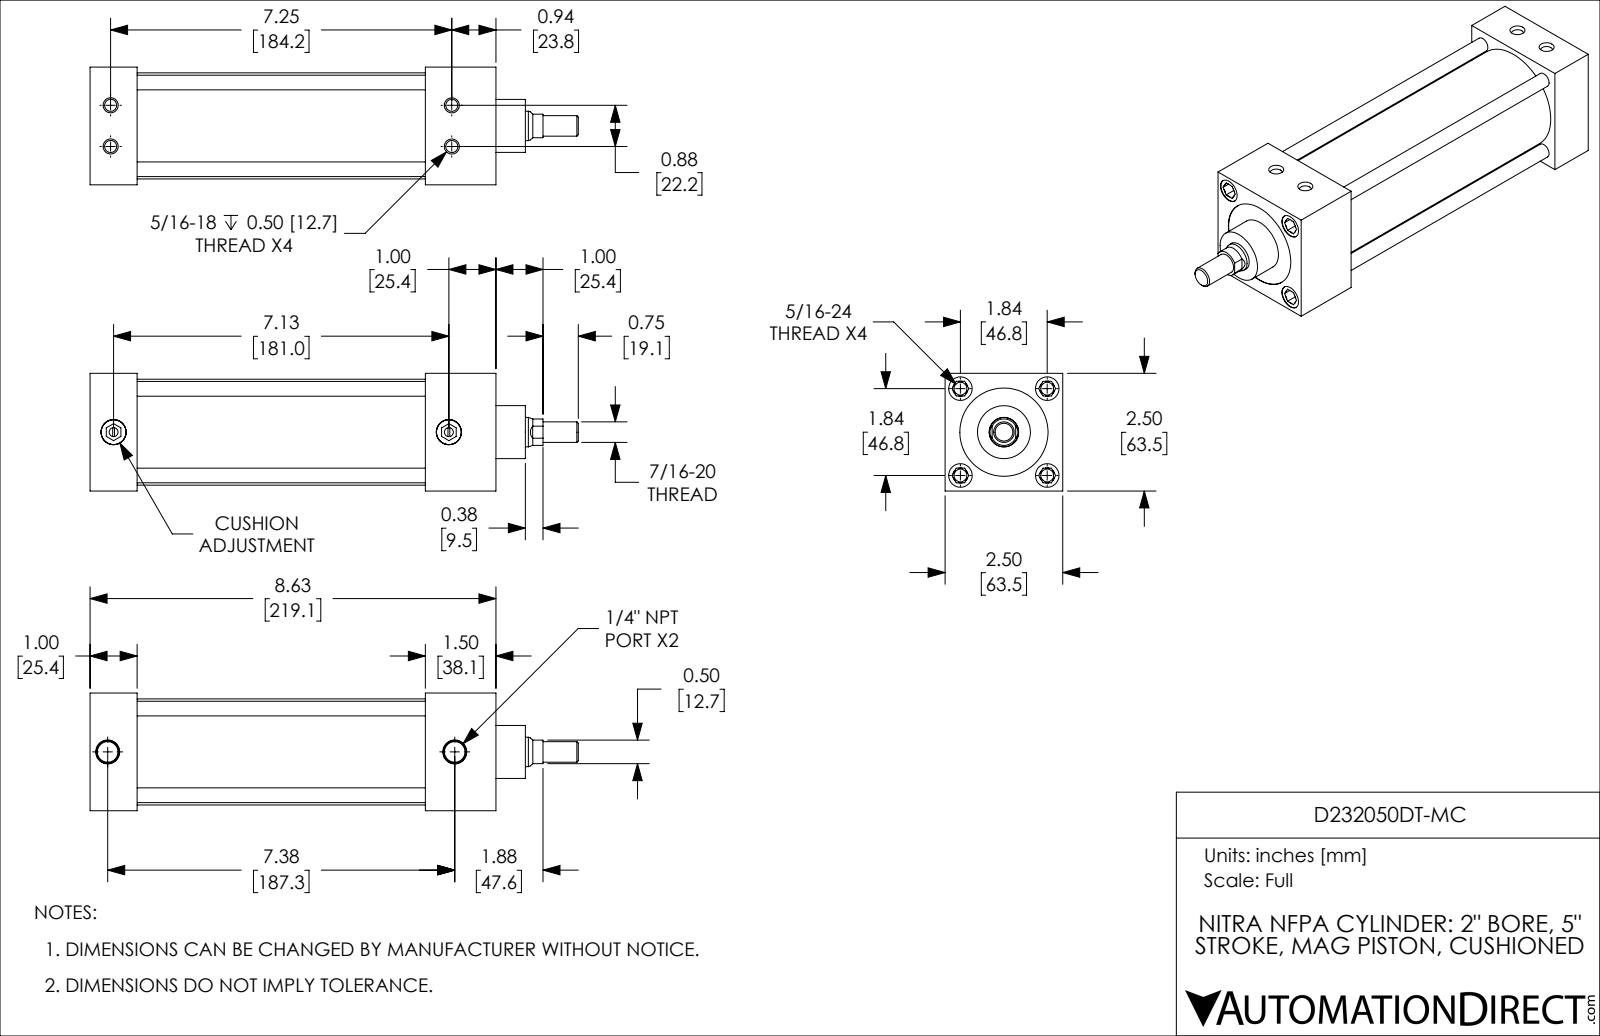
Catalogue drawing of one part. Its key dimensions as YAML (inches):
part_name: "D232050DT-MC; D232050DT-MC_PISTON_KK1; D232050DT-MC_BODY; D232050DT-MC_CUSHION"
step_written_by: "SolidWorks 2019 (CONFIG_CONTROL_DESIGN)"
units: inches
bodies: {solids: 4, faces: 248, planar: 90, cylindrical: 78, other: 80}
overall_size: [10.375, 2.5, 2.5]
volume: 27.66
surface_area: 200.1
round_holes:
  - {diameter: 0.272, count: 7}
  - {diameter: 0.257, count: 4}
  - {diameter: 0.5, count: 4}
  - {diameter: 0.19, count: 2}
  - {diameter: 0.438, count: 2}
  - {diameter: 0.531, count: 2}
  - {diameter: 0.626, count: 1}
  - {diameter: 1.875, count: 1}
  - {diameter: 2.001, count: 1}
round_bosses_or_shafts:
  - {diameter: 0.312, count: 4}
  - {diameter: 0.532, count: 2}
  - {diameter: 2.251, count: 1}
  - {diameter: 1.999, count: 1}
  - {diameter: 1.125, count: 1}
  - {diameter: 0.624, count: 1}
  - {diameter: 0.437, count: 1}
partial_cylinders:
  - {radius: 0.281, count: 1}
face_to_face_distances: [2.5, 1, 7.125, 6.125, 1.125, 2.125, 5, 1.5, 8.625, 7.625]
hole_center_spacings: [1.84, 1.844, 1.301, 0.441, 0.443, 0.875, 1.304, 2.602]
